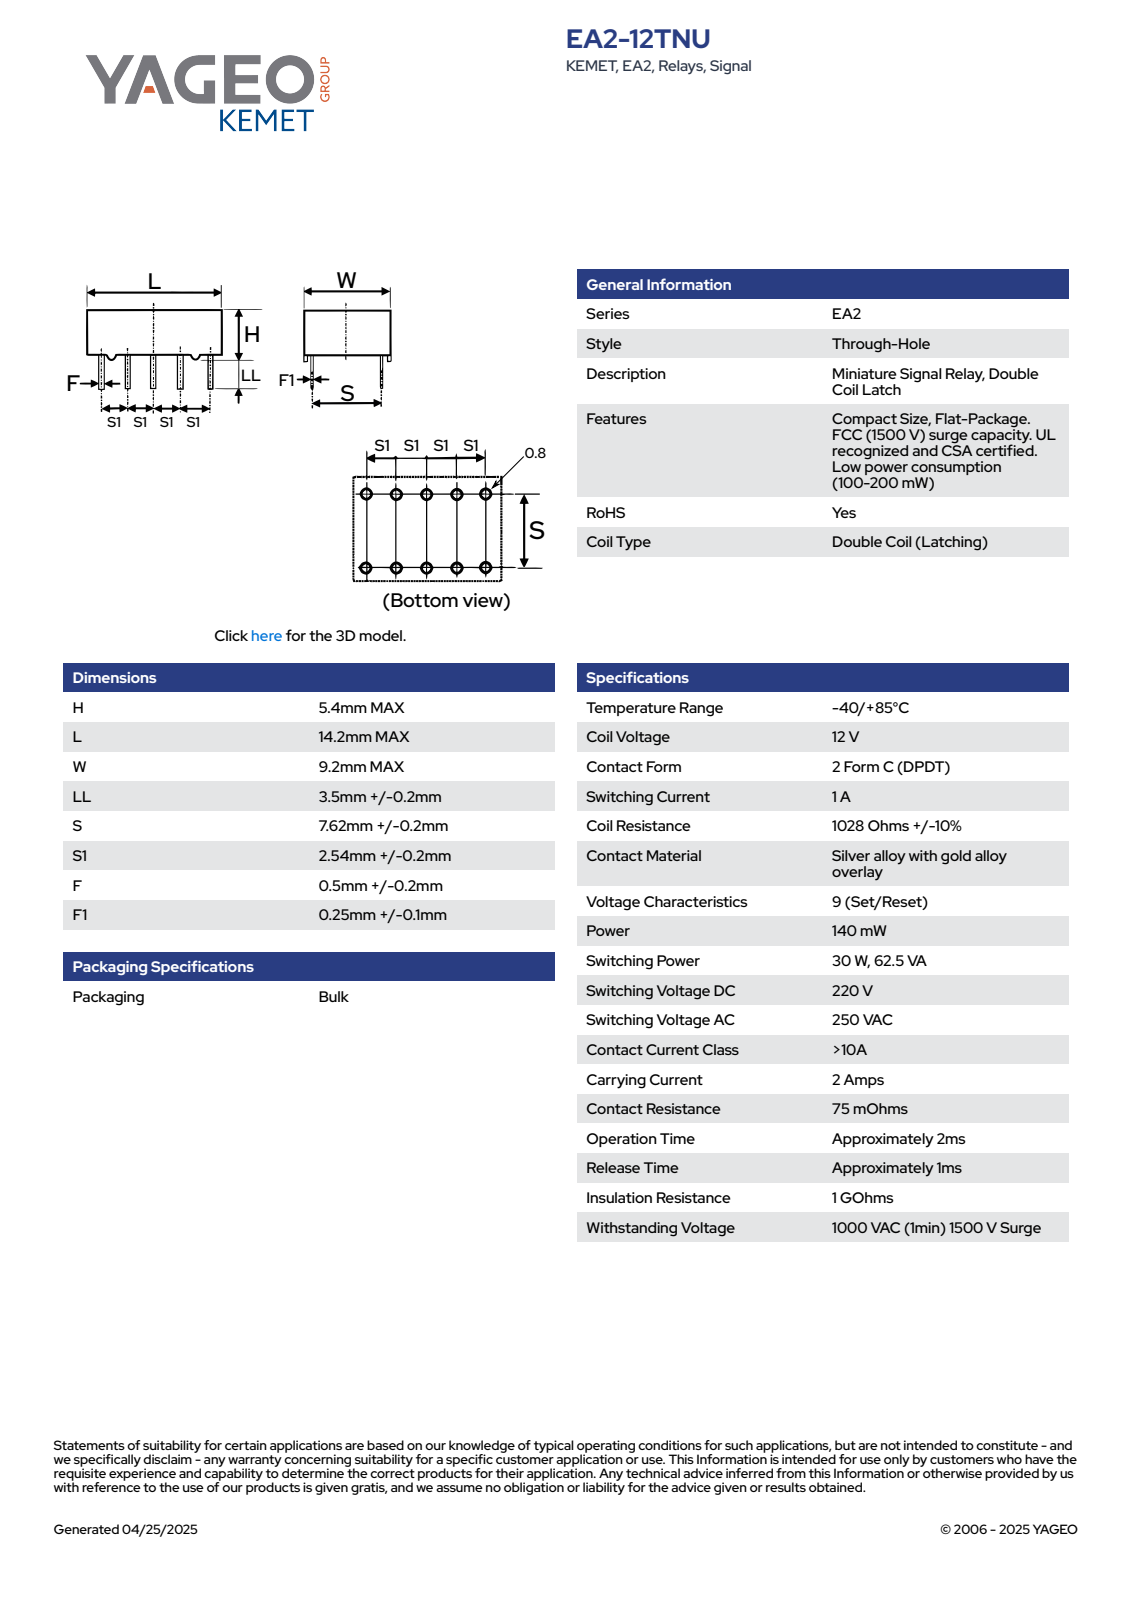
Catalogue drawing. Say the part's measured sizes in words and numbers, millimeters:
The part is named "IR_TEA2_L14.2W9.2H5.4". Its 3-D file was written by "SolidWorks 2014 (AUTOMOTIVE_DESIGN)". It is 1 solid with 118 faces: 114 planar, 4 cylindrical and 0 other. Overall it measures 14.2 by 9.2 by 9.1 millimeters. Its volume is 670 cubic millimeters and its surface area 585 square millimeters. Partial cylindrical surfaces (rounded edges, fillets, slot ends): 2 of radius 0.35. The main face-to-face distances are 5.05, 9.2, 14.2, 7.62, 0.35, 2.54, 0.61, 0.96, 8.24, 8.59.
